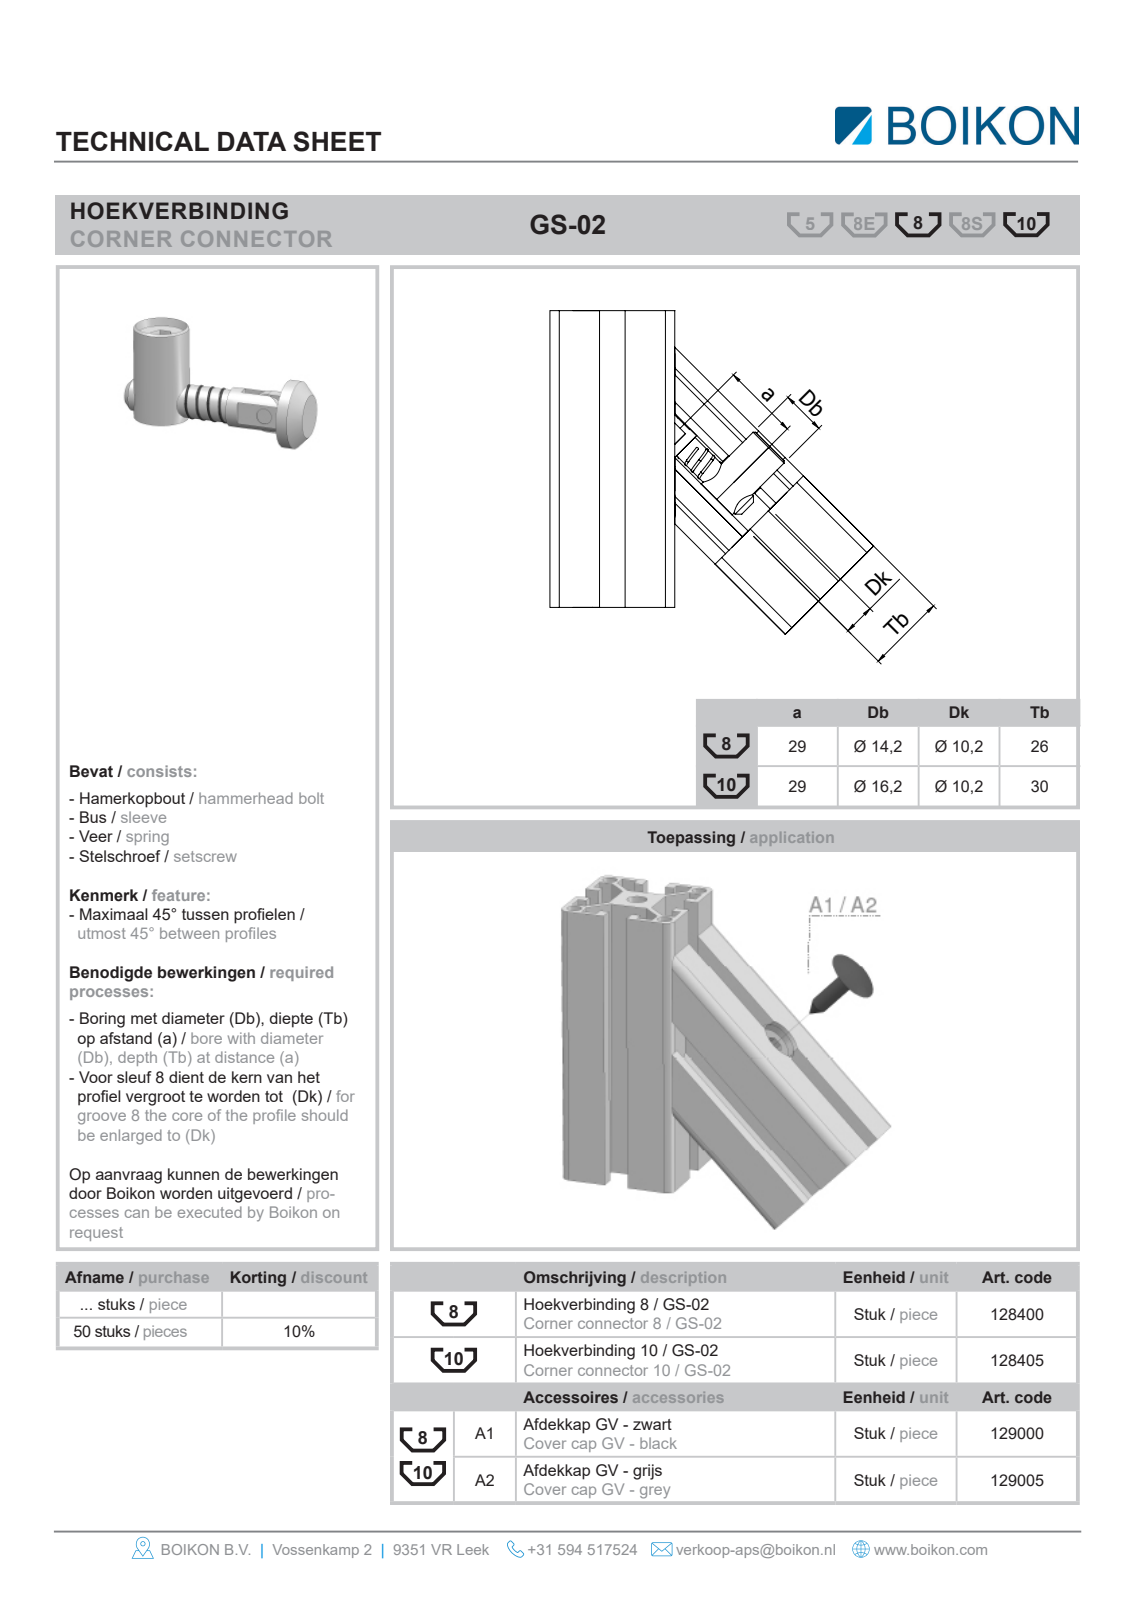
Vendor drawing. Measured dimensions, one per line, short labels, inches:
name: Root; 128405Hoekverbinding 10 / GS-02BOIKON
written by: HiCAD 2013 1802.4 Build 509 (AUTOMOTIVE_DESIGN)
unit: in
bodies: 3 solids, 42 faces (26 planar, 13 cylindrical, 3 other)
size: 1.98 × 1.24 × 0.787
volume: 0.526 in³; area: 6.688 in²
holes: 1× ⌀0.157, 1× ⌀0.161
bosses: 1× ⌀0.787, 1× ⌀0.63, 1× ⌀0.386, 1× ⌀0.327
rounds: 1× R0.185, 1× R0.193
face distances: 1.142, 0.114, 0.22, 0.236, 0.096, 0.1, 0.211, 0.215, 0.11, 0.118
